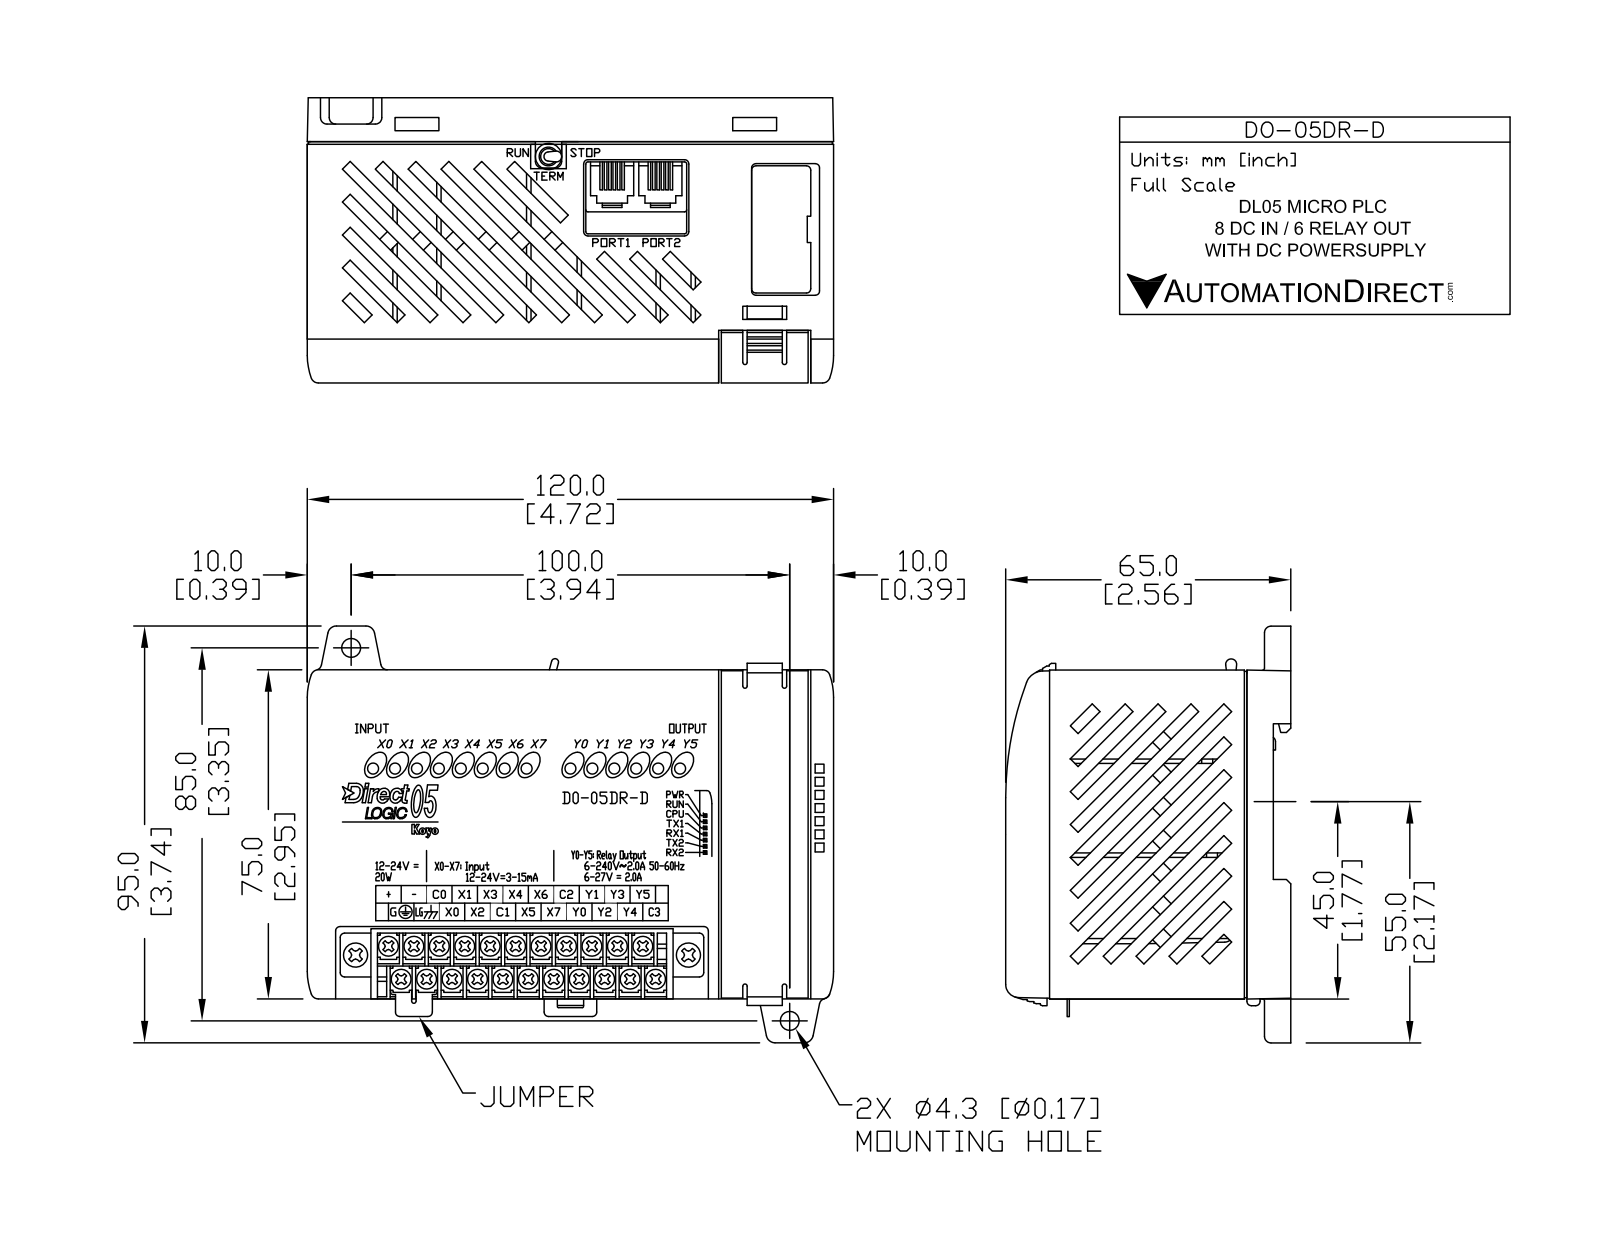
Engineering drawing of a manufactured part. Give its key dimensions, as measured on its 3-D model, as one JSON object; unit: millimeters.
{"part_name": "D0-05DR-D", "step_written_by": "SolidWorks 2009 (AUTOMOTIVE_DESIGN)", "units": "millimeters", "bodies": {"solids": 3, "faces": 1012, "planar": 689, "cylindrical": 95, "other": 228}, "overall_size": [120, 95, 65.06], "volume_mm3": 65415, "surface_area_mm2": 91010, "round_holes": [[4.3, 2]], "round_bosses_or_shafts": [[4.42, 22], [4.5, 2]], "partial_cylinders_radius": [[1, 4], [2, 4], [1.5, 2], [63.5, 1], [65, 1]], "face_to_face_distances": [1.5, 73.5, 59.5, 4, 63.5, 118.5, 75, 72, 5.5, 65], "hole_center_spacings": [131.24]}
